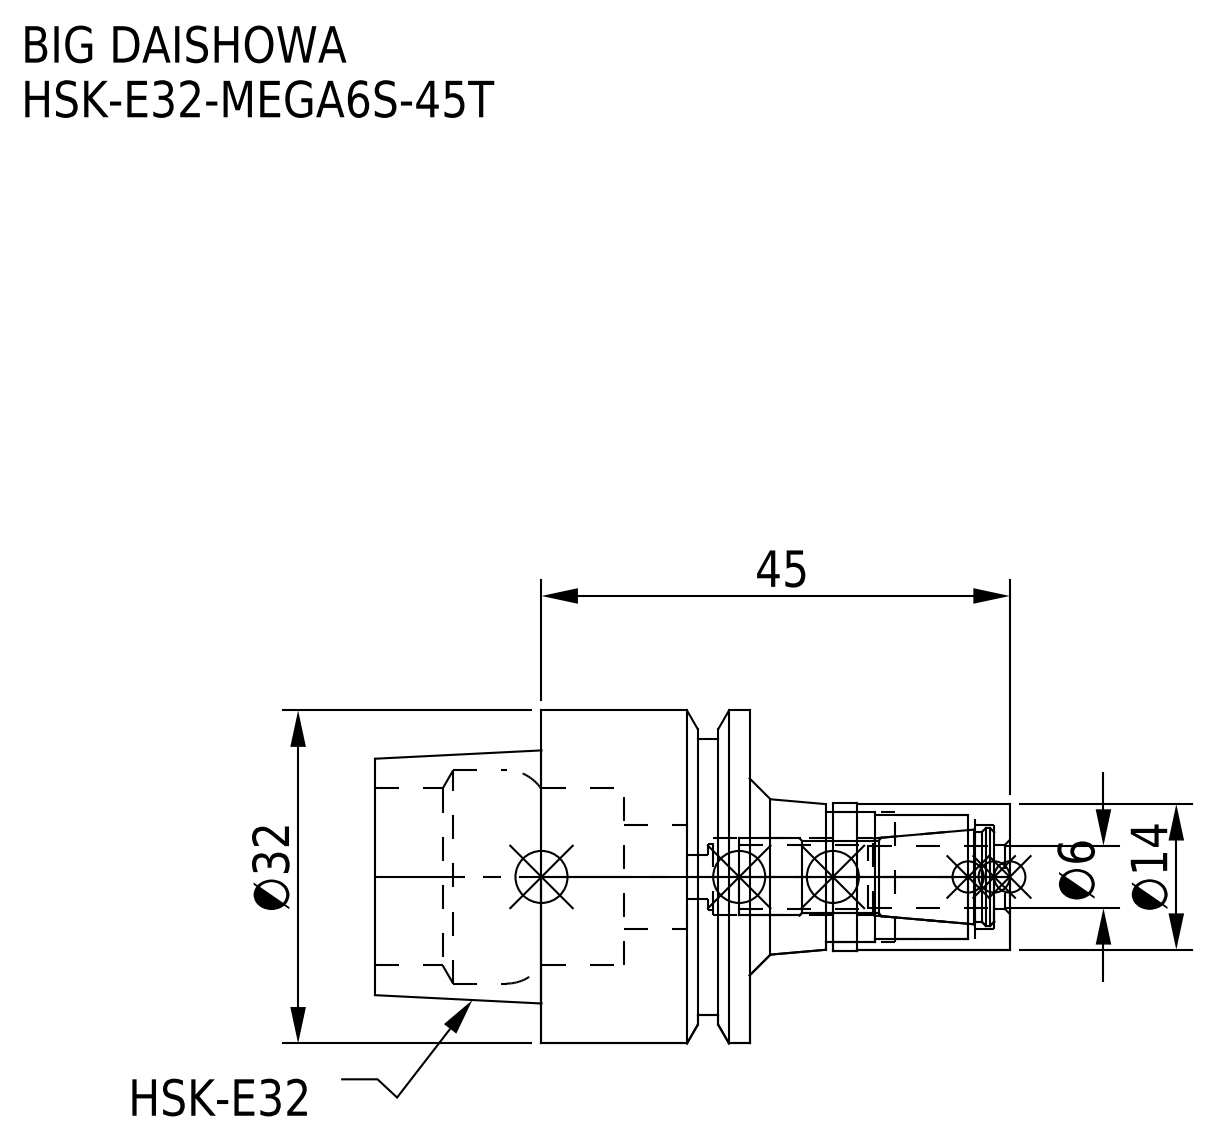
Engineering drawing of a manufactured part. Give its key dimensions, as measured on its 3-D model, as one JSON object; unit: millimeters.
{"part_name": "HE32MS06045T-060_ASM.stp; DXF_TEMP_ASSY_ASM_4_ASM.stp; MGN6S_1.stp; HSK-E32-MEGA6S-45T (+3 more)", "step_written_by": "SolidWorks 2019 (CONFIG_CONTROL_DESIGN)", "units": "millimeters", "bodies": {"solids": 2, "faces": 74, "planar": 18, "cylindrical": 38, "other": 18}, "overall_size": [61, 32, 32], "volume_mm3": 18203, "surface_area_mm2": 9699, "round_holes": [[4.2, 1], [6.1, 1], [6.4, 1], [7.4, 1], [10, 1], [12, 1], [12.5, 1], [17, 1], [20.5, 1]], "round_bosses_or_shafts": [[32, 1], [26.5, 1], [14.3, 1], [14, 1]], "face_to_face_distances": [20, 16, 36, 12.05, 7.95, 23.95, 17, 25, 28, 37.05]}
